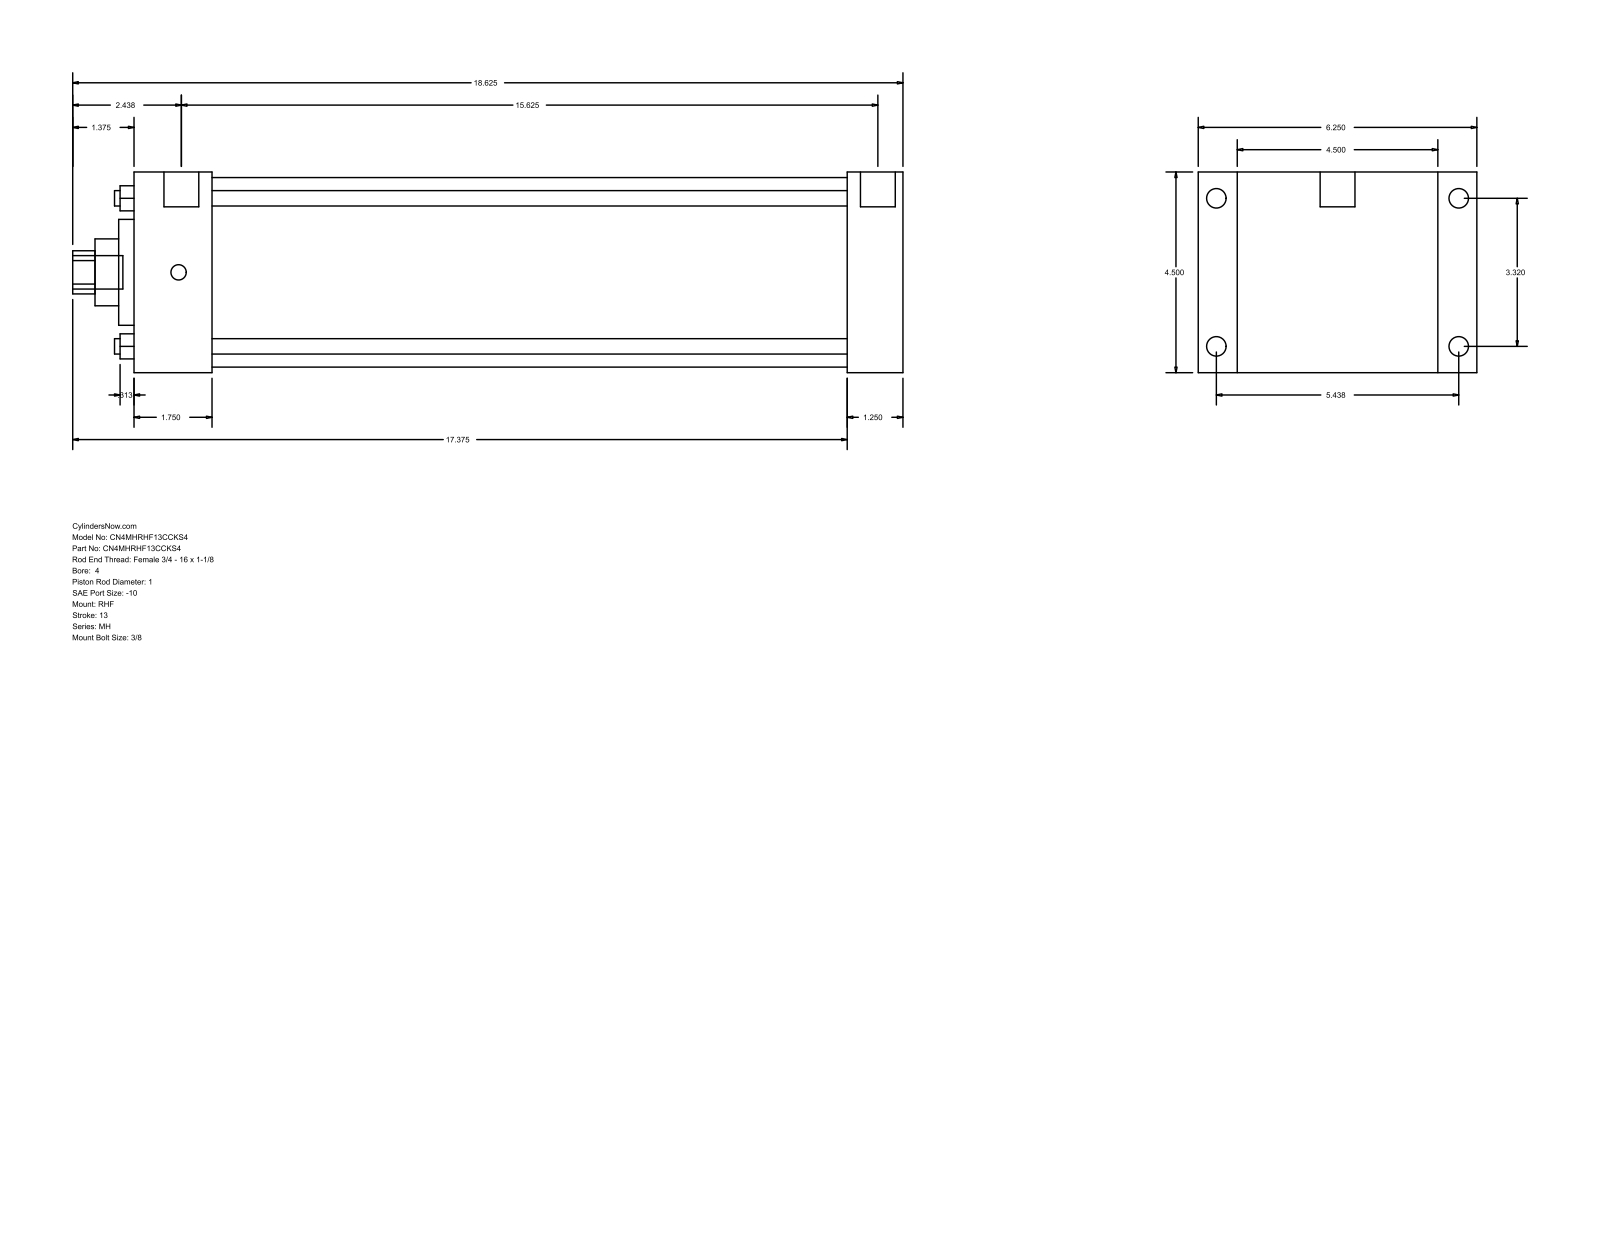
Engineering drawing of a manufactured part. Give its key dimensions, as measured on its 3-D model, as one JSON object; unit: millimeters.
{"part_name": "MH_RHF__0400_1", "step_written_by": "GSSL Pune (CONFIG_CONTROL_DESIGN)", "units": "millimeters", "bodies": {"solids": 0, "faces": 90, "planar": 61, "cylindrical": 29, "other": 0}, "overall_size": [473.07, 158.75, 114.3], "round_holes": [[8.76, 4], [25.4, 1], [38.1, 1], [60.33, 1], [107.95, 1]], "round_bosses_or_shafts": [[11.13, 4], [8.73, 4], [19.84, 2], [19.05, 1]], "partial_cylinders_radius": [[12.29, 1]], "face_to_face_distances": [114.3, 438.15, 406.4, 31.75, 22.23, 136.53, 44.46, 361.94, 393.69, 158.76], "hole_center_spacings": [59.62, 84.32, 119.25]}
